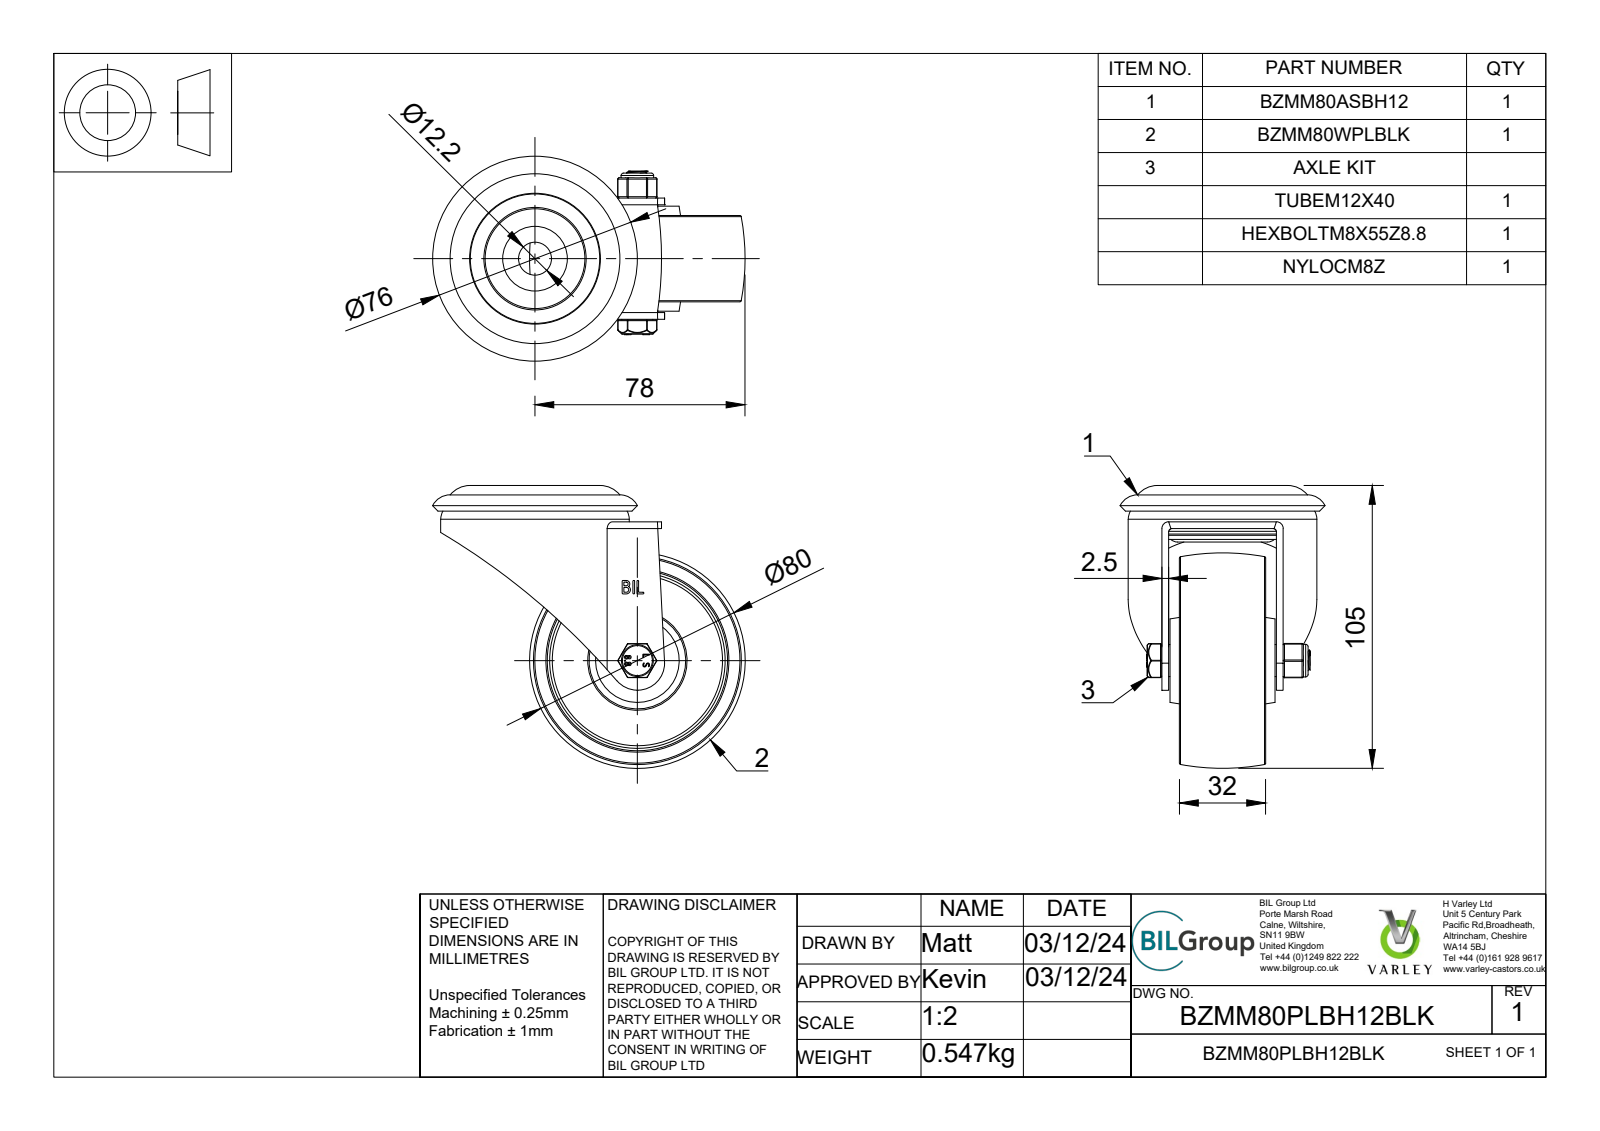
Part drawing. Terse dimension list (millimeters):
name: BZMM80PLBH12BLK v3; BZMM80ASBH12 v1; ZINC PLATED, PRESSED STEEL FORKS; ZINC PLATED, PRESSED STEEL TOP PLATE (+8 more)
written by: Autodesk Translation Framework v13.20.0.188 (AP242_MANAGED_MODEL_BASED_3D_ENGINEERING_MIM_LF)
unit: mm
bodies: 7 solids, 341 faces (109 planar, 124 cylindrical, 108 other)
size: 116 × 105 × 76
volume: 151 897 mm³; area: 72 003 mm²
holes: 2× ⌀0.66, 2× ⌀12.2, 1× ⌀8, 1× ⌀8.2, 1× ⌀8.4, 1× ⌀8.6, 1× ⌀65, 1× ⌀72
bosses: 1× ⌀70, 1× ⌀49.5, 1× ⌀38, 1× ⌀24, 1× ⌀21.31, 1× ⌀12.1, 1× ⌀11.9, 1× ⌀11.5
rounds: 18× R0.5, 12× R0.25, 4× R0.33, 4× R0.64, 4× R1.25, 2× R0.63, 2× R0.64, 2× R2.5
face distances: 2.5, 7, 4, 6.5, 19, 26, 16.5, 42.5, 23.5, 36
hole spacings: 3.22, 2.49
